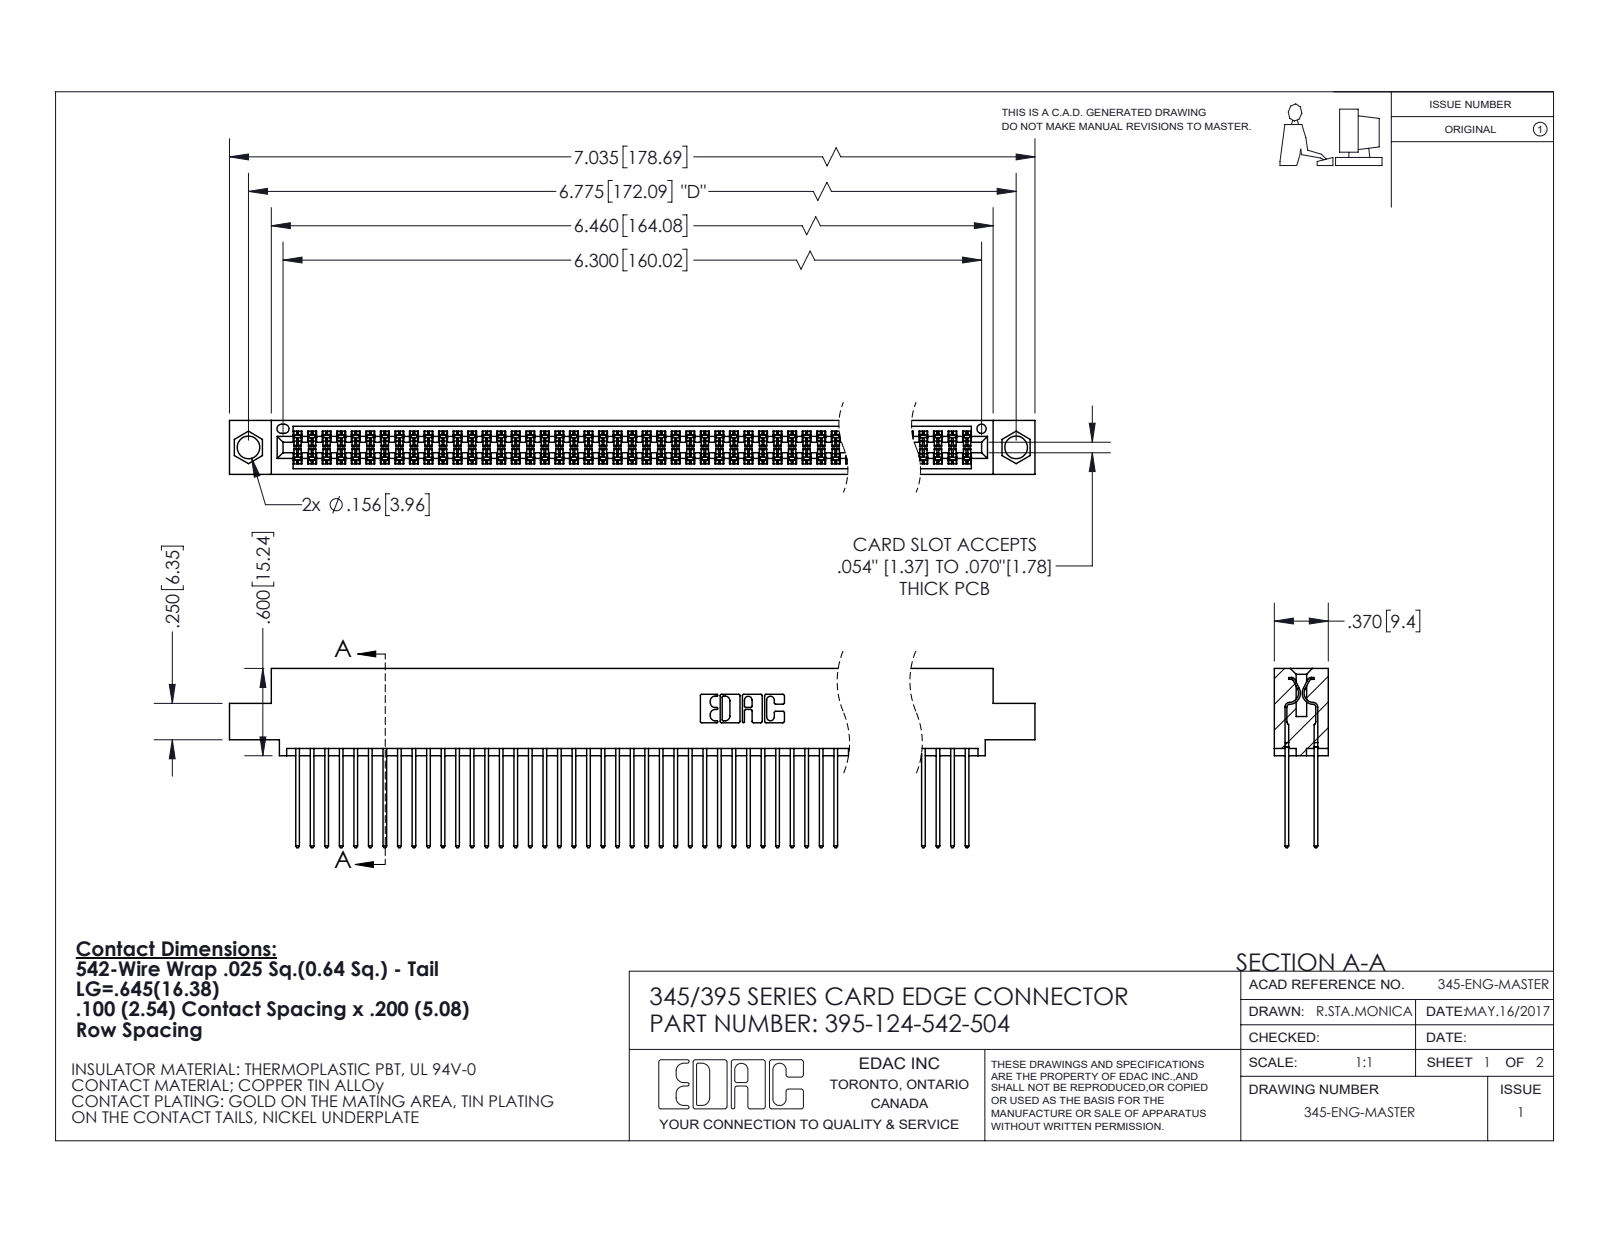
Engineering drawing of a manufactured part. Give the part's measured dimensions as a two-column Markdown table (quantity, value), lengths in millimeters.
| quantity | value |
| --- | --- |
| part name | 345 Part_0.110 Offset - 0.156 Dia-TI; 395-124-542-504; 345-292-001_345-293-142 |
| STEP written by | SolidWorks 2020 (CONFIG_CONTROL_DESIGN) |
| units | millimeters |
| bodies | 125 solids, 6344 faces (4190 planar, 2154 cylindrical, 0 other) |
| overall size | 178.7 × 31.3 × 9.4 |
| volume | 17 940 mm³ |
| surface area | 29 550 mm² |
| round holes (diameter × count) | 4 × 2, 1.6 × 1 |
| partial cylindrical surfaces (radius × count) | 0.2 × 186, 0.3 × 124, 0.3 × 22, 0.2 × 6, 0.8 × 6, 0.7 × 3, 0.4 × 2, 0.5 × 2 |
| main face-to-face distances | 1.8, 7.6, 5.1, 2.5, 6.9, 0.6, 5.7, 9.4, 4.4, 3.8 |
| hole center spacings | 6.9, 166.1, 172.1 |
